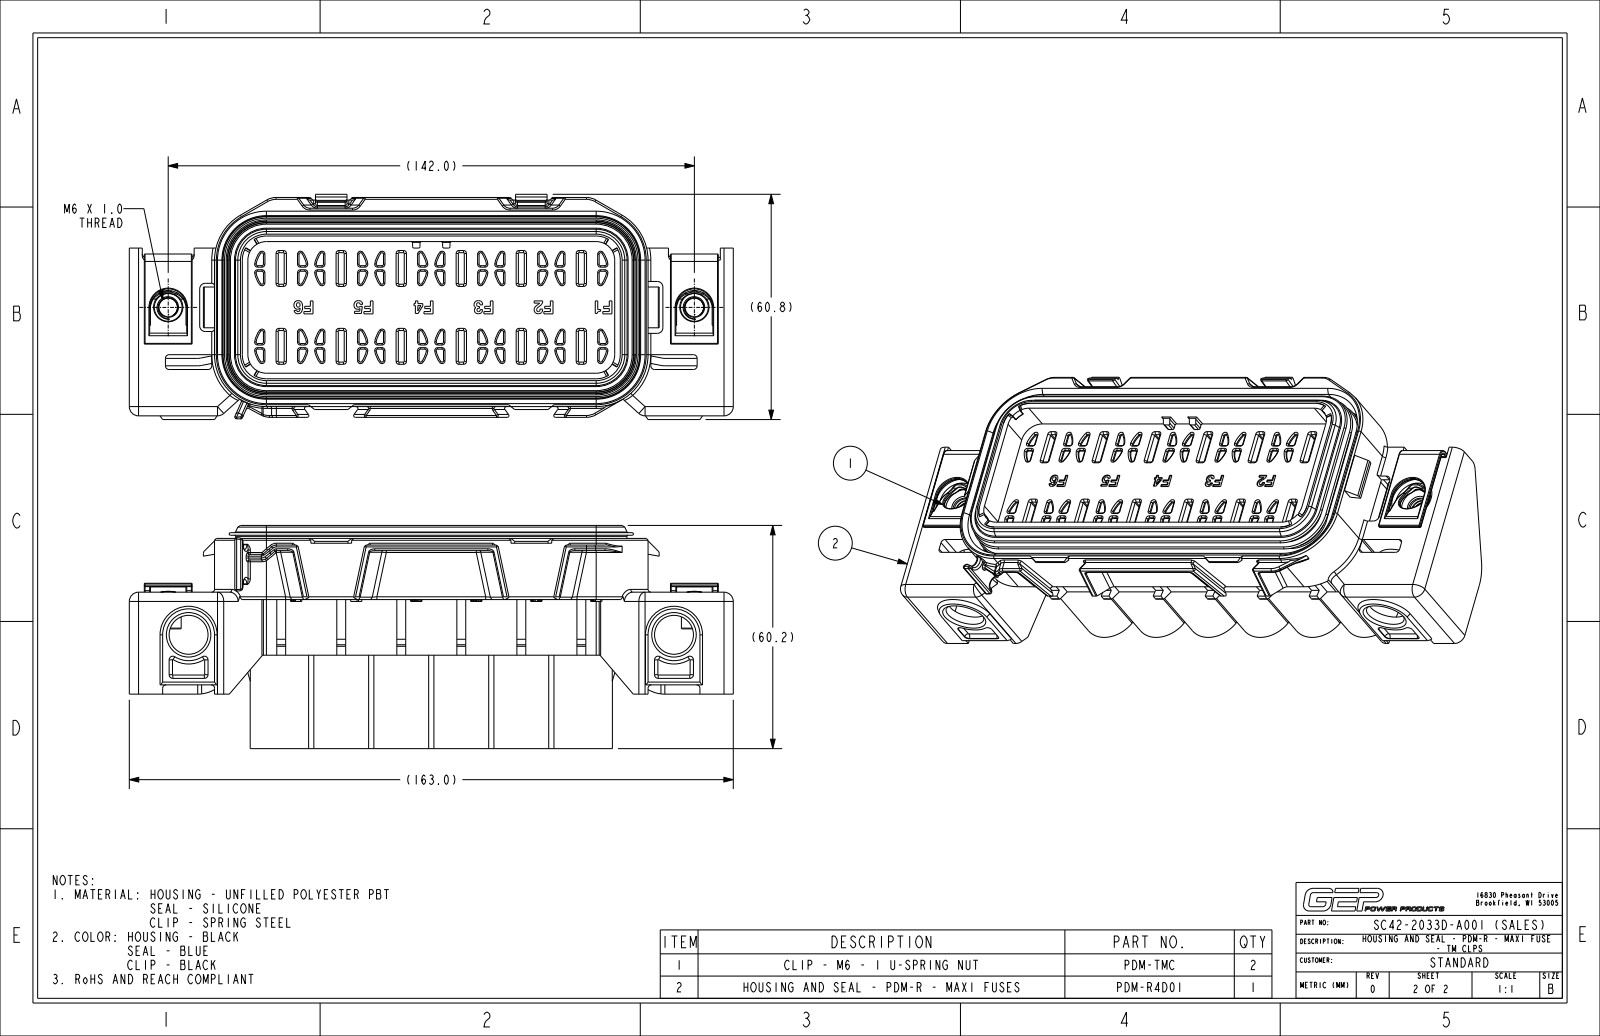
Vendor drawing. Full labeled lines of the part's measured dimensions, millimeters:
Part name (STEP PRODUCT): C26-1012-2D_SALES_NCF; C14-1013_INSTALLED_NCF; PDM-RS_INSTALLED_NCF_ASM; PDM-R4D01_NCF_ASM (+3 more)
STEP written by: CREO PARAMETRIC BY PTC INC, 2024014 (CONFIG_CONTROL_DESIGN)
Units: millimetres
Bodies: 4 solids, 3619 faces (1729 planar, 995 cylindrical, 895 other)
Overall size (bounding box): 163 × 60.76 × 60.2
Volume: 153 065 mm³ · Surface area: 117 546 mm²
Round holes (diameter × count): ⌀13.75 ×12, ⌀10.5 ×4, ⌀5 ×2, ⌀7.5 ×2, ⌀12.5 ×2
Round bosses / shafts (diameter × count): ⌀6.35 ×5, ⌀7 ×2, ⌀5 ×1, ⌀2.5 ×1
Partial cylindrical surfaces — rounded edges, fillets, slot ends (radius × count): R0.4 ×157, R0.5 ×148, R0.2 ×116, R0.8 ×47, R0.3 ×46, R0.9 ×39, R1 ×26, R0.35 ×16
Main face-to-face distances: 2, 16.2, 38.5, 1.5, 9.5, 32.4, 11.5, 2.5, 37, 1.8
Hole centre spacings: 16.2, 26.52, 32.4, 38.61, 21, 48.6, 52.94, 32.26
